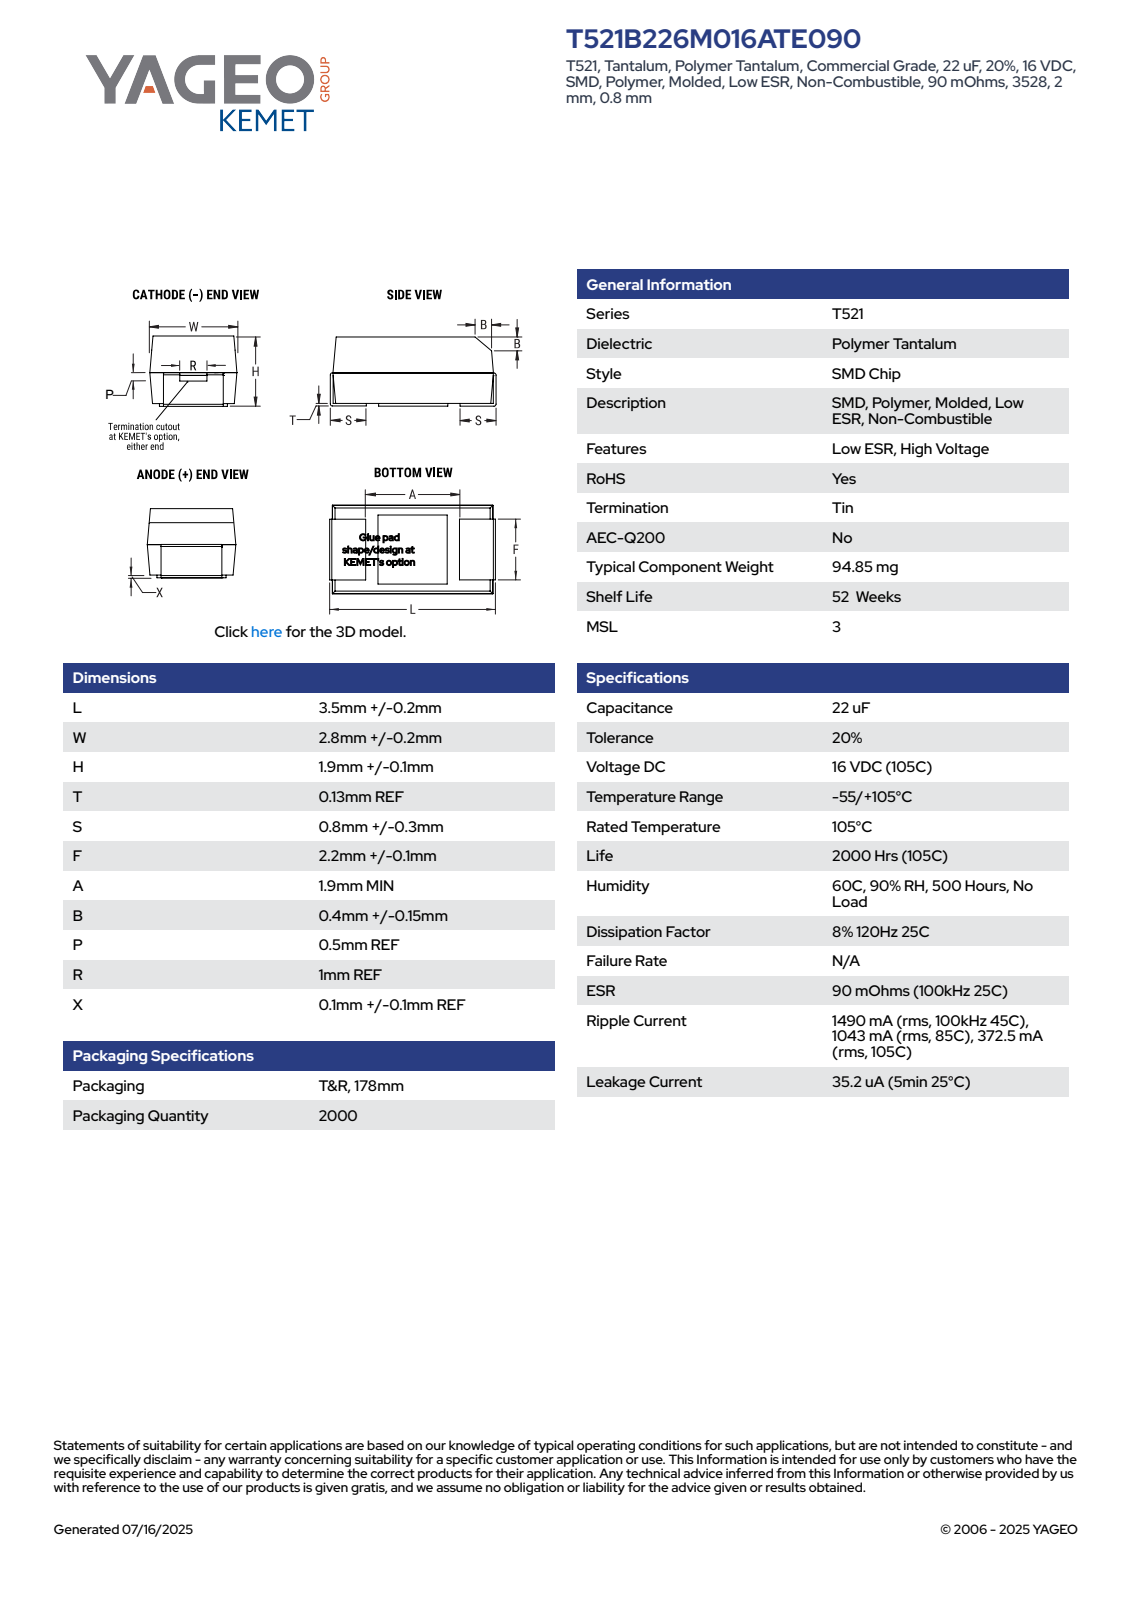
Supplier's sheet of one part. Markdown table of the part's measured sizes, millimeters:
| quantity | value |
| --- | --- |
| part name | CTSM_TCM2NKKO_3528_L3.7W3H2T0.13S0.8F2.3A1.9B0.55P0.5R1X0.1 |
| STEP written by | SolidWorks 2021 (AUTOMOTIVE_DESIGN) |
| units | millimeters |
| bodies | 4 solids, 100 faces (95 planar, 5 cylindrical, 0 other) |
| overall size | 3.7 × 3 × 2.04 |
| volume | 19 mm³ |
| surface area | 51 mm² |
| partial cylindrical surfaces (radius × count) | 0.1 × 4 |
| main face-to-face distances | 2.96, 2, 2.03, 1.9, 3.57, 3.7, 3.44, 0.37, 0.67, 0.8 |
